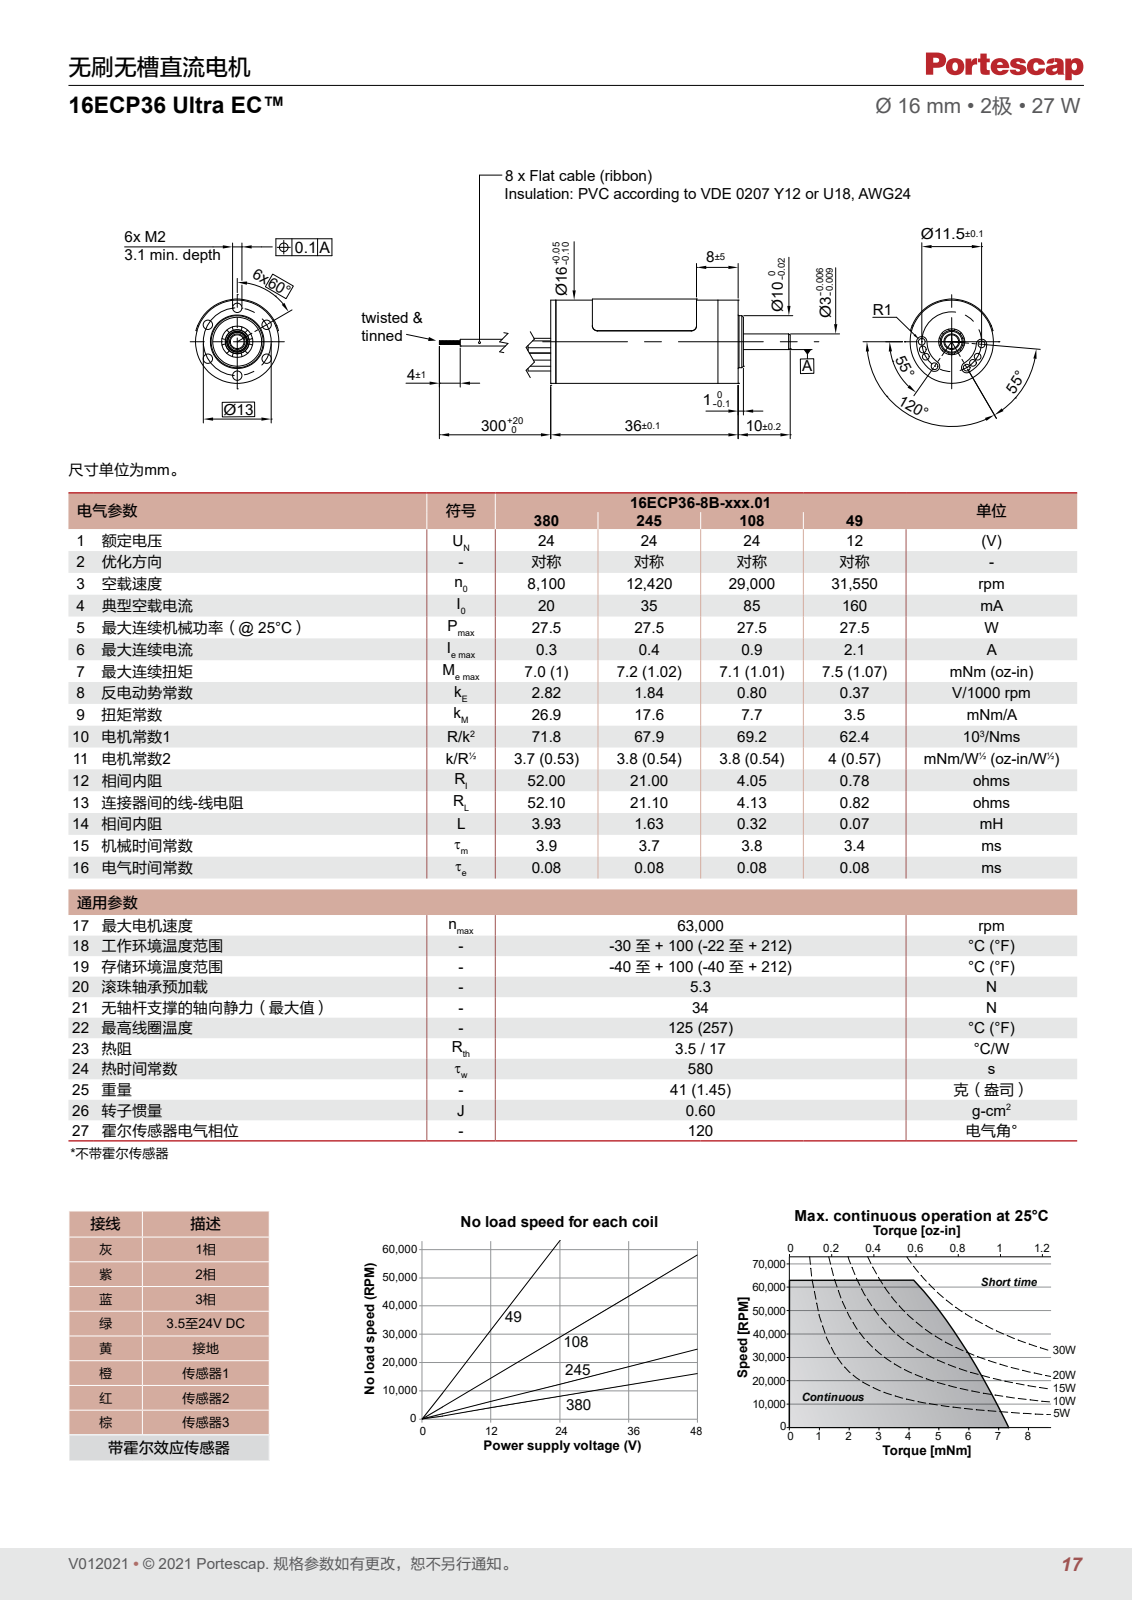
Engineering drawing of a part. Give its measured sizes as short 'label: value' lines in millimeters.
name: 16ECP36_ULTRA_EC_ASM
written by: PRO/ENGINEER BY PARAMETRIC TECHNOLOGY CORPORATION, 2014310 (CONFIG_CONTROL_DESIGN)
unit: mm
bodies: 1 solid, 252 faces (39 planar, 103 cylindrical, 110 other)
size: 121 × 16.2 × 16
volume: 7 942 mm³; area: 5 959 mm²
holes: 6× ⌀1.6, 1× ⌀5, 1× ⌀5.6, 1× ⌀6, 1× ⌀6.4, 1× ⌀7, 1× ⌀8, 1× ⌀15
bosses: 8× ⌀1.3, 8× ⌀0.7, 1× ⌀16, 1× ⌀10, 1× ⌀4.6, 1× ⌀4.4, 1× ⌀3
rounds: 8× R1, 1× R4.75, 1× R6.75, 1× R8.2
face distances: 3.6, 36, 3.5, 32.5, 32.4, 0.5, 28.5, 32.1, 28.6, 3.9
hole spacings: 6.5, 11.26, 13
